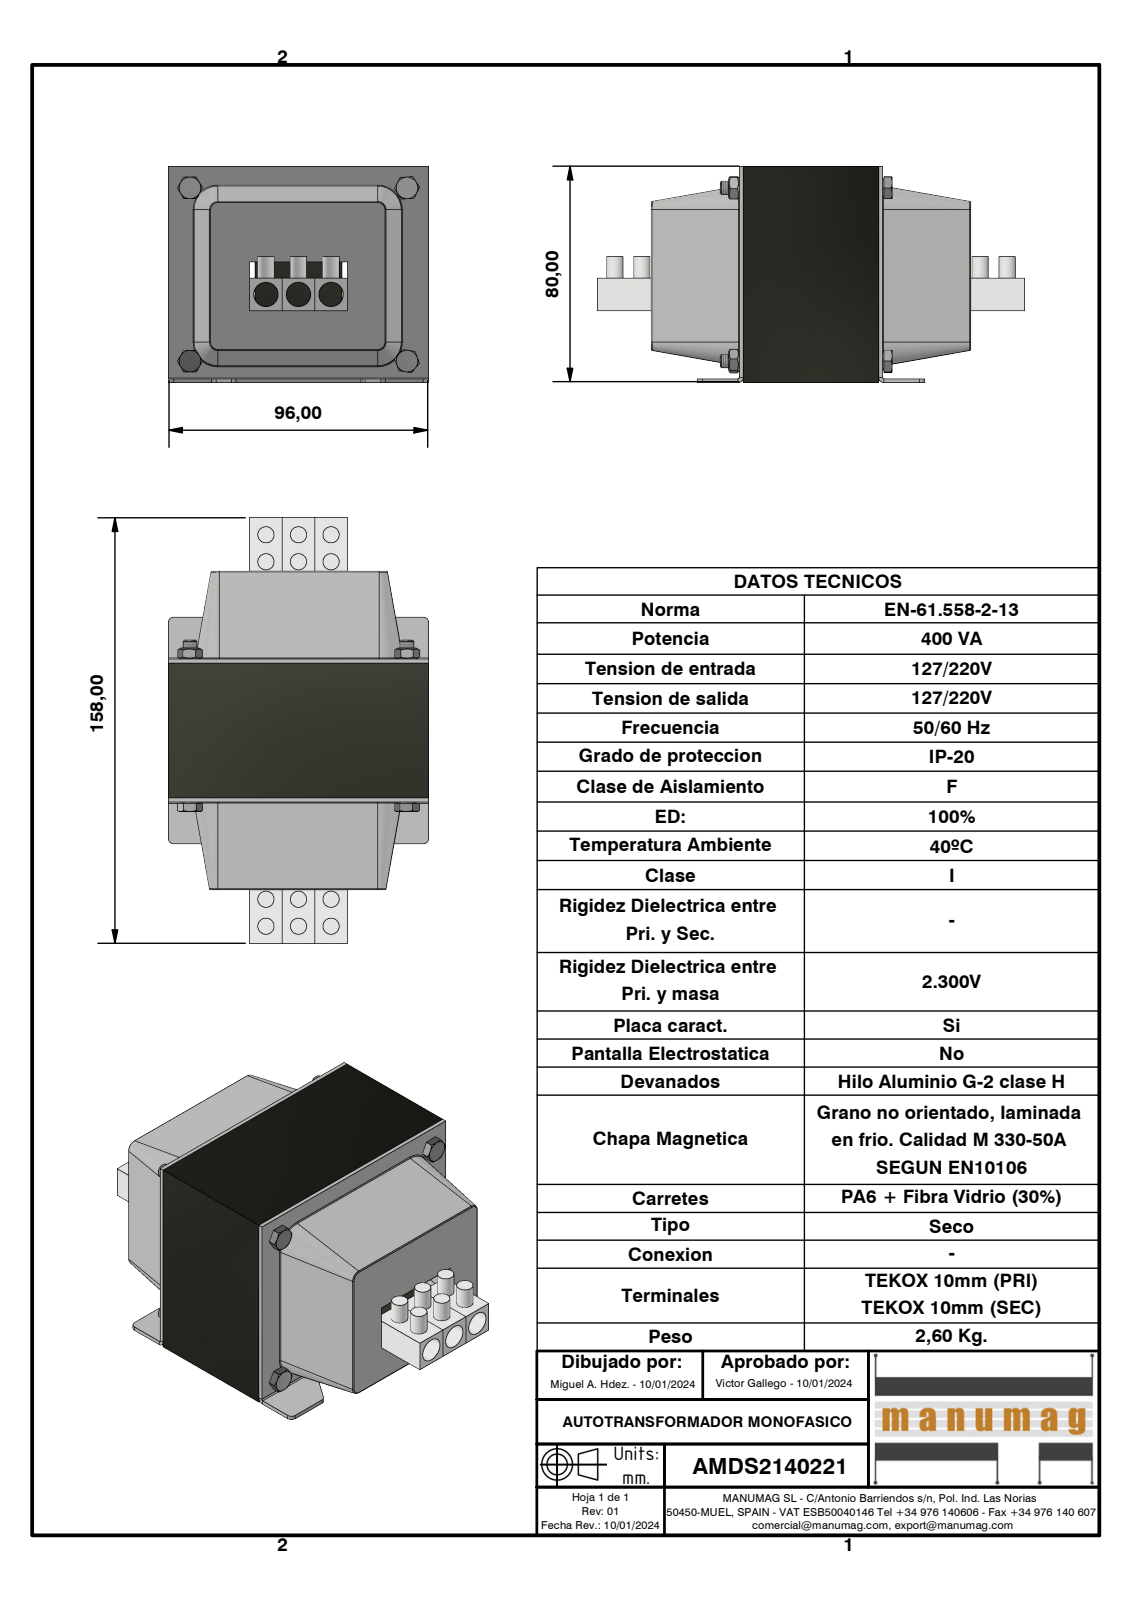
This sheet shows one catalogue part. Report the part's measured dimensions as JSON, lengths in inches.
{"part_name": "AMDS2140221; DIN 933 - M5 x 60; DIN 934 - M5 x 0,8; TAPA RC32 VENTANA 3 ELEMENTOS 10 CON FICHAS (+4 more)", "step_written_by": "Autodesk Inventor 2023 (AUTOMOTIVE_DESIGN)", "units": "inches", "bodies": {"solids": 17, "faces": 352, "planar": 194, "cylindrical": 78, "other": 80}, "overall_size": [6.22, 3.78, 3.15], "volume_in3": 21.1, "surface_area_in2": 194.1, "round_holes": [[0.163, 4], [0.197, 4], [0.217, 4], [0.354, 3]], "round_bosses_or_shafts": [[0.236, 12], [0.264, 4], [0.18, 4]], "partial_cylinders_radius": [[0.015, 16], [0.079, 14], [0.02, 2]], "face_to_face_distances": [0.059, 0.63, 1.28, 3.307, 2.52, 3.15, 1.969, 1.26, 1.339, 1.89], "hole_center_spacings": [0.472, 1.468, 1.849, 1.902, 2.209, 2.265, 2.52, 2.568]}
